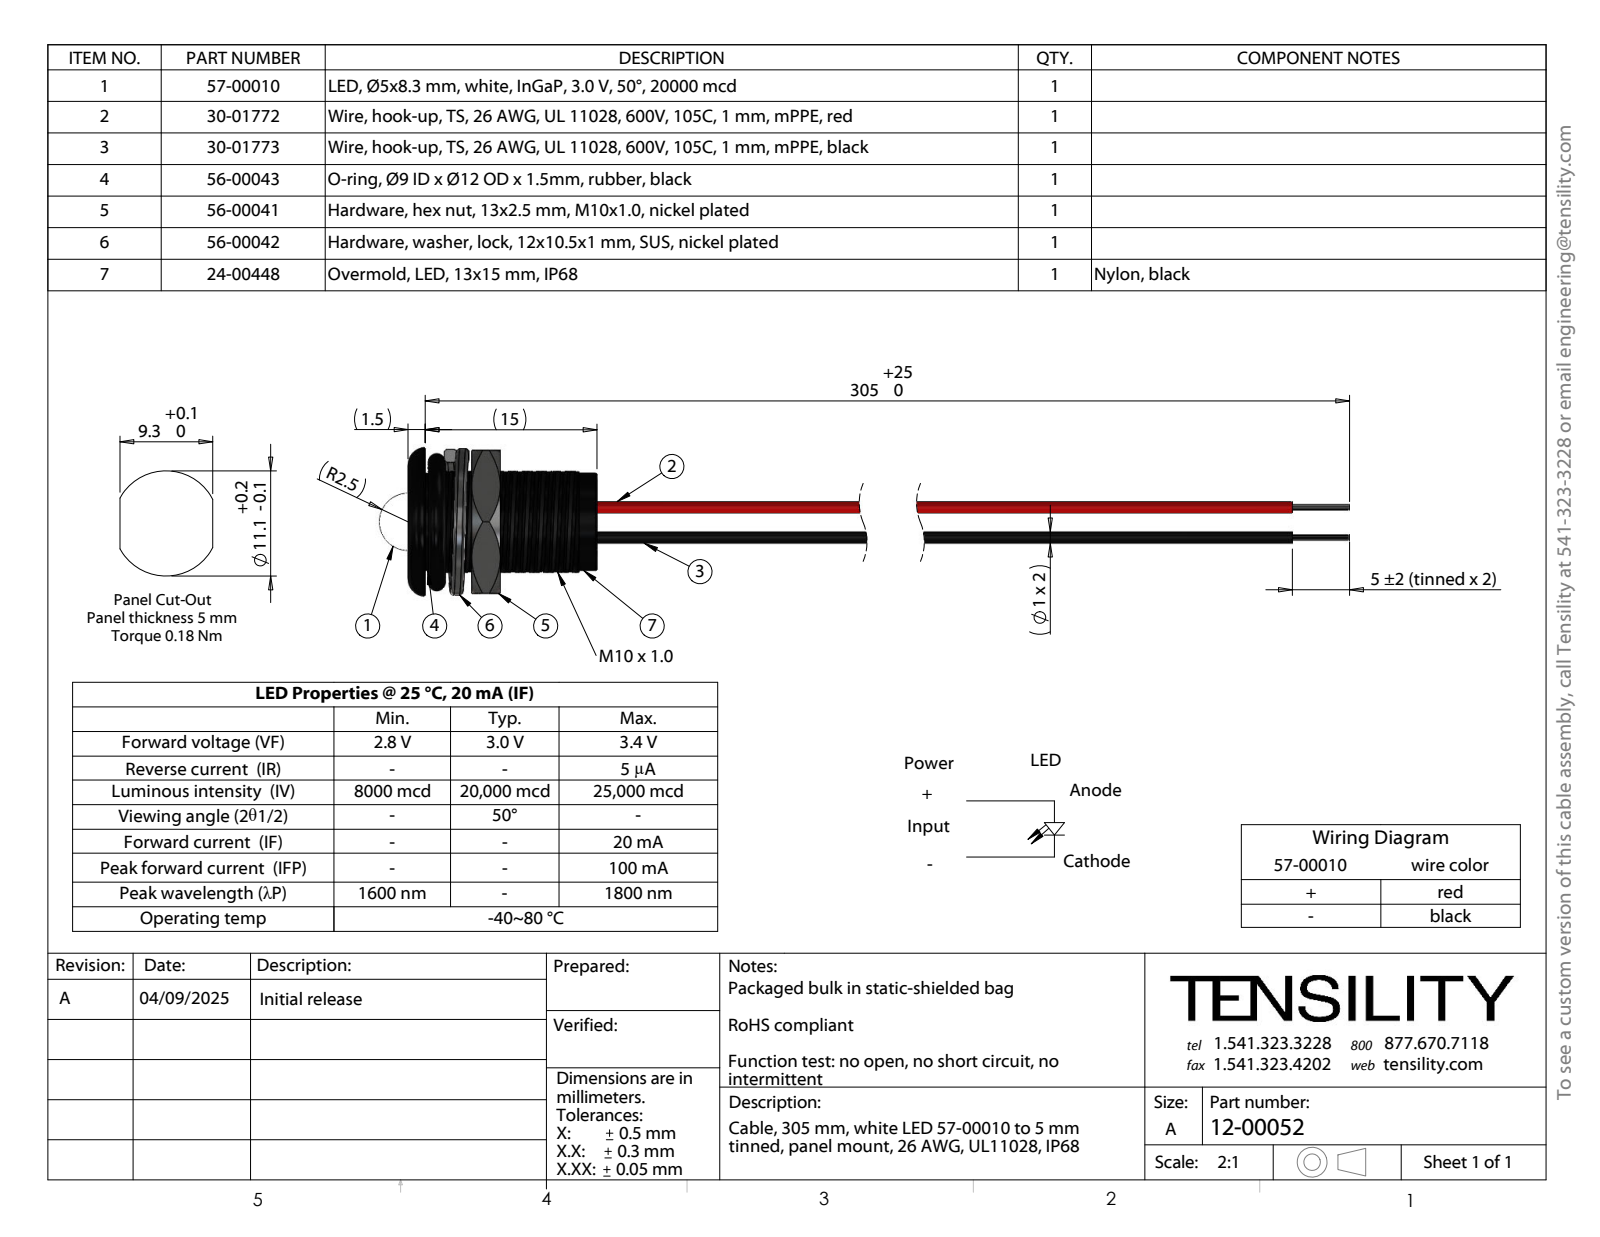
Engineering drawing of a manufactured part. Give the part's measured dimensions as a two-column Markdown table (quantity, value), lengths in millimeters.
| quantity | value |
| --- | --- |
| part name | 57-00010_trimmed leads; 12-00052; 24-00448; 56-00043 (+4 more) |
| STEP written by | SolidWorks 2021 (CONFIG_CONTROL_DESIGN) |
| units | millimeters |
| bodies | 57 solids, 514 faces (185 planar, 246 cylindrical, 83 other) |
| overall size | 173.99 × 14.43 × 12.99 |
| volume | 1 769 mm³ |
| surface area | 6 568 mm² |
| round holes (diameter × count) | 1 × 2 |
| round bosses / shafts (diameter × count) | 1 × 2, 0.83 × 2, 8.5 × 1, 5 × 1 |
| partial cylindrical surfaces (radius × count) | 4.33 × 1, 5 × 1 |
| main face-to-face distances | 1.5, 16.5, 15, 12.5, 8.06, 6.56, 8.44, 5.56, 4.06, 2.5 |
| hole center spacings | 0.36, 0.38, 0.33, 2.43, 2.35, 2.48, 2.52, 2.56 |
